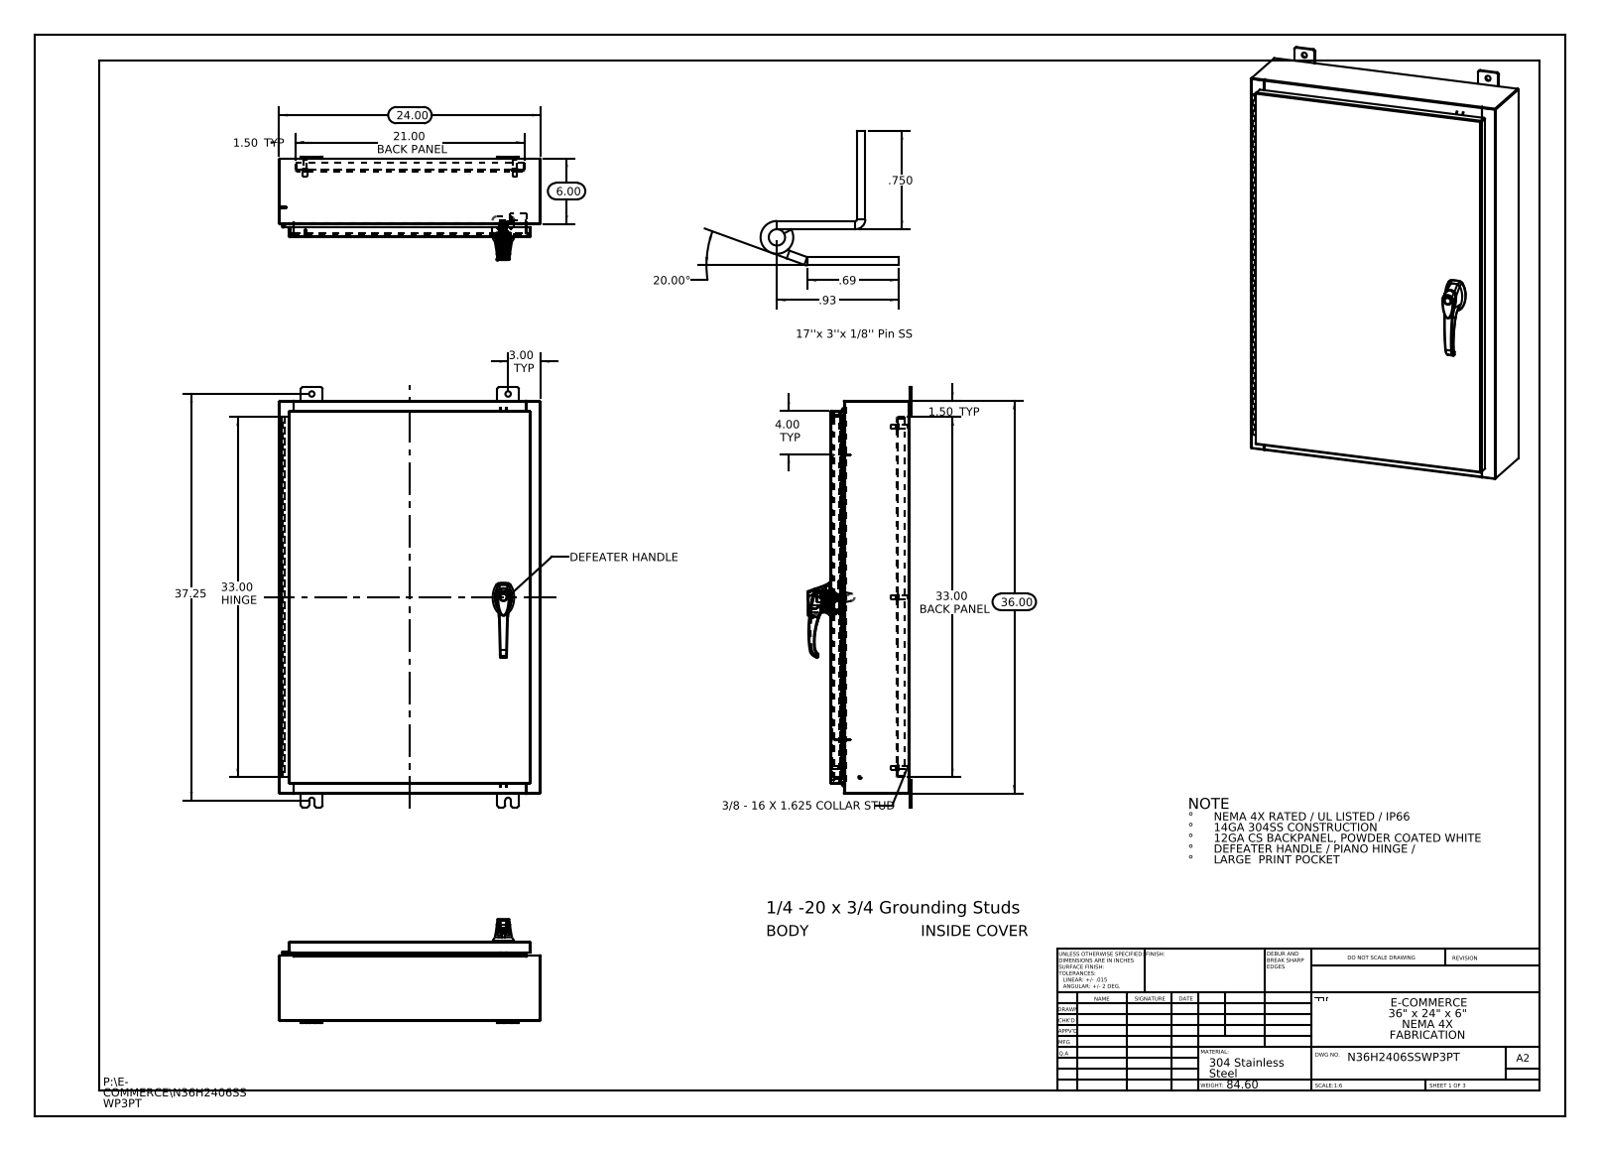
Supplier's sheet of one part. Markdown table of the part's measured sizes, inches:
| quantity | value |
| --- | --- |
| part name | N36H2406SSWP3PT Top; Quarter-20 CD Stud; g26103103_26163303; N36H2406SSWP3PT Hinge Enclosure Side2 (+8 more) |
| STEP written by | SolidWorks 2013 (CONFIG_CONTROL_DESIGN) |
| units | inches |
| bodies | 39 solids, 2856 faces (1053 planar, 1085 cylindrical, 718 other) |
| overall size | 38.5 × 24 × 9.495 |
| volume | 300.7 in³ |
| surface area | 7 381 in² |
| round holes (diameter × count) | 0.5 × 10, 0.25 × 4, 0.138 × 3, 0.161 × 3, 0.079 × 2, 0.203 × 2, 0.313 × 2, 0.437 × 2, 0.125 × 1, 0.125 × 1, 0.197 × 1, 0.276 × 1 |
| round bosses / shafts (diameter × count) | 0.625 × 6, 0.375 × 6, 0.33 × 6, 0.157 × 4, 0.14 × 4, 0.315 × 3, 0.236 × 3, 1.181 × 1 |
| partial cylindrical surfaces (radius × count) | 0.118 × 37, 0.006 × 33, 0.013 × 24, 0.19 × 24, 0.088 × 18, 0.039 × 15, 0.028 × 12, 0.008 × 6 |
| main face-to-face distances | 0.075, 7.126, 0.104, 7.051, 7.201, 1, 1.075, 6.051, 6.126, 1.179 |
| hole center spacings | 11.363, 13.669, 15.625, 24.793, 19.25, 0.295, 0.625, 0.841 |
